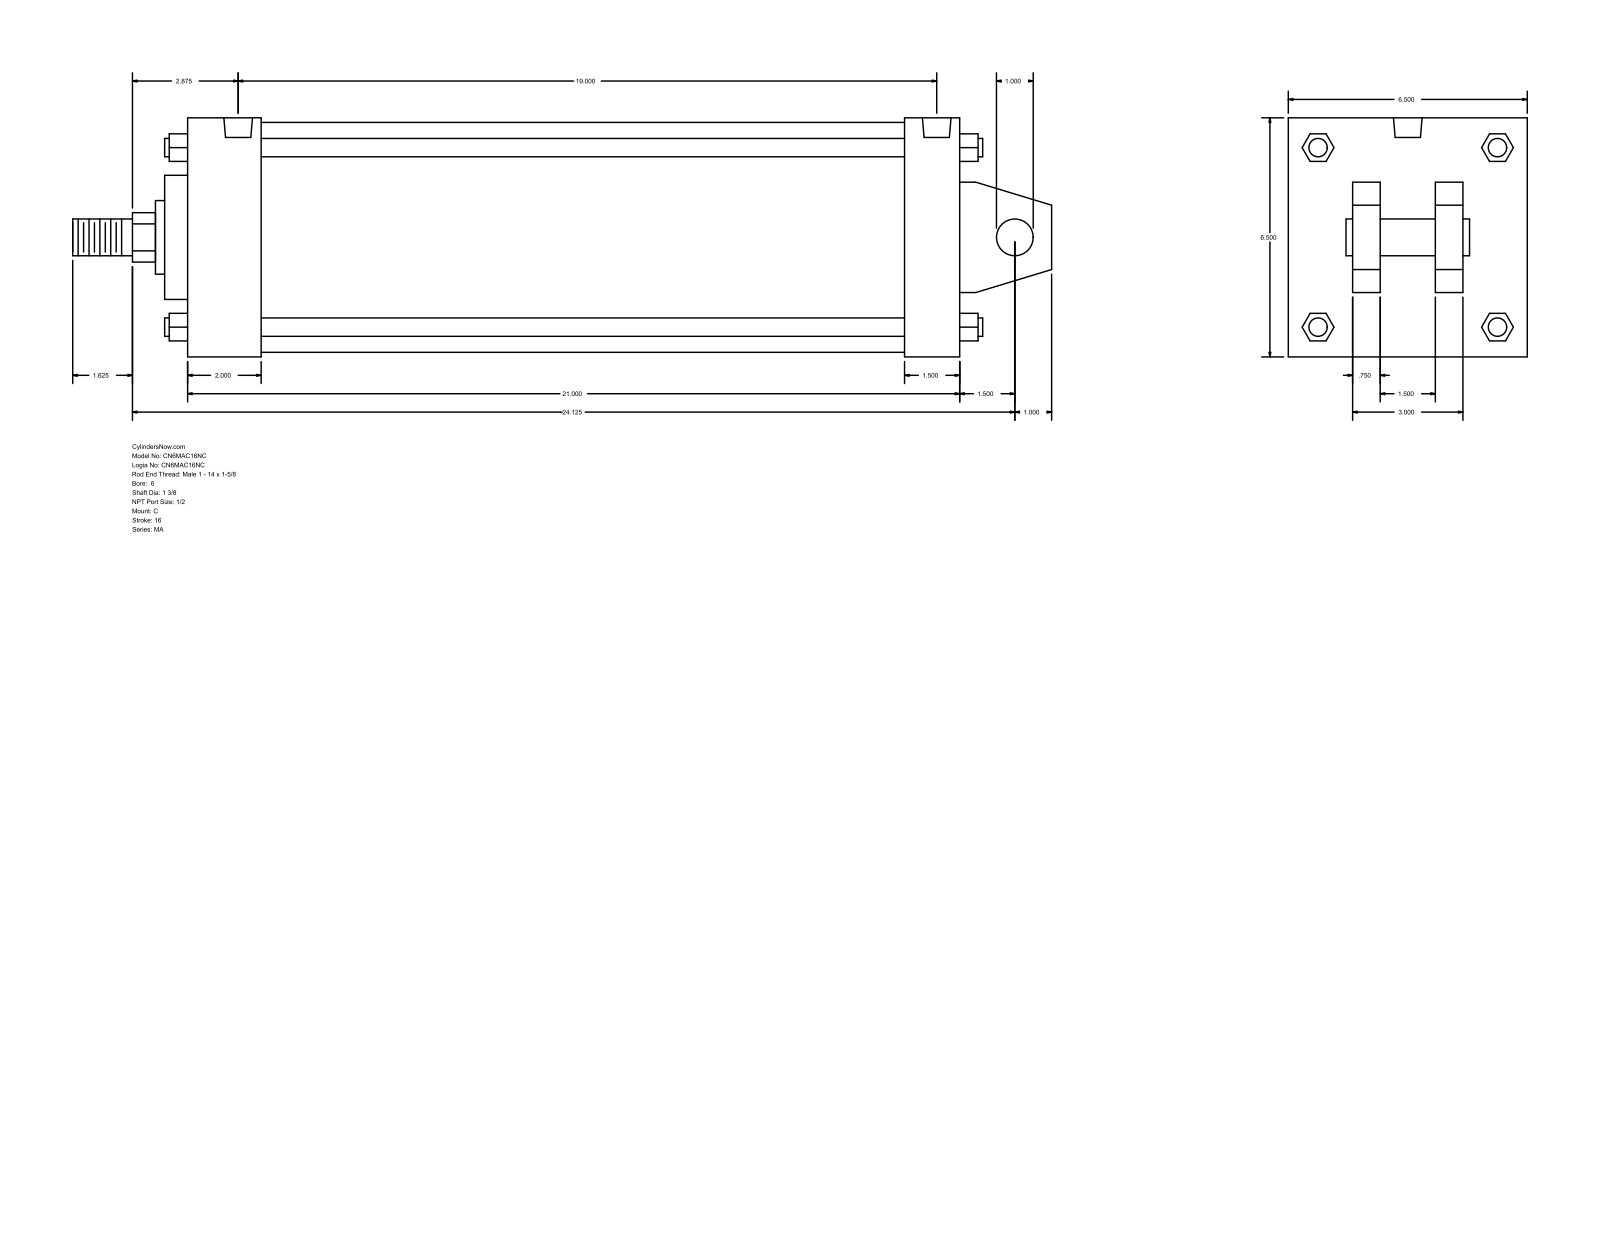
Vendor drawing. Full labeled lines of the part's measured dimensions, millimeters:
Part name (STEP PRODUCT): MA_C__0600_1.375
STEP written by: GSSL Pune (CONFIG_CONTROL_DESIGN)
Units: millimetres
Bodies: 0 solids, 141 faces (109 planar, 32 cylindrical, 0 other)
Overall size (bounding box): 676.27 × 165.1 × 165.1
Round holes (diameter × count): ⌀17.46 ×4, ⌀19.77 ×2
Round bosses / shafts (diameter × count): ⌀12.7 ×4, ⌀25.4 ×2, ⌀158.75 ×1, ⌀85.72 ×1, ⌀50.8 ×1, ⌀34.92 ×1
Partial cylindrical surfaces — rounded edges, fillets, slot ends (radius × count): R17.06 ×1
Main face-to-face distances: 165.1, 533.4, 38.1, 19.05, 63.5, 101.6, 50.8, 44.45, 120.65, 495.3
Hole centre spacings: 482.6, 3.17, 3.18, 479.42, 482.59, 485.77
